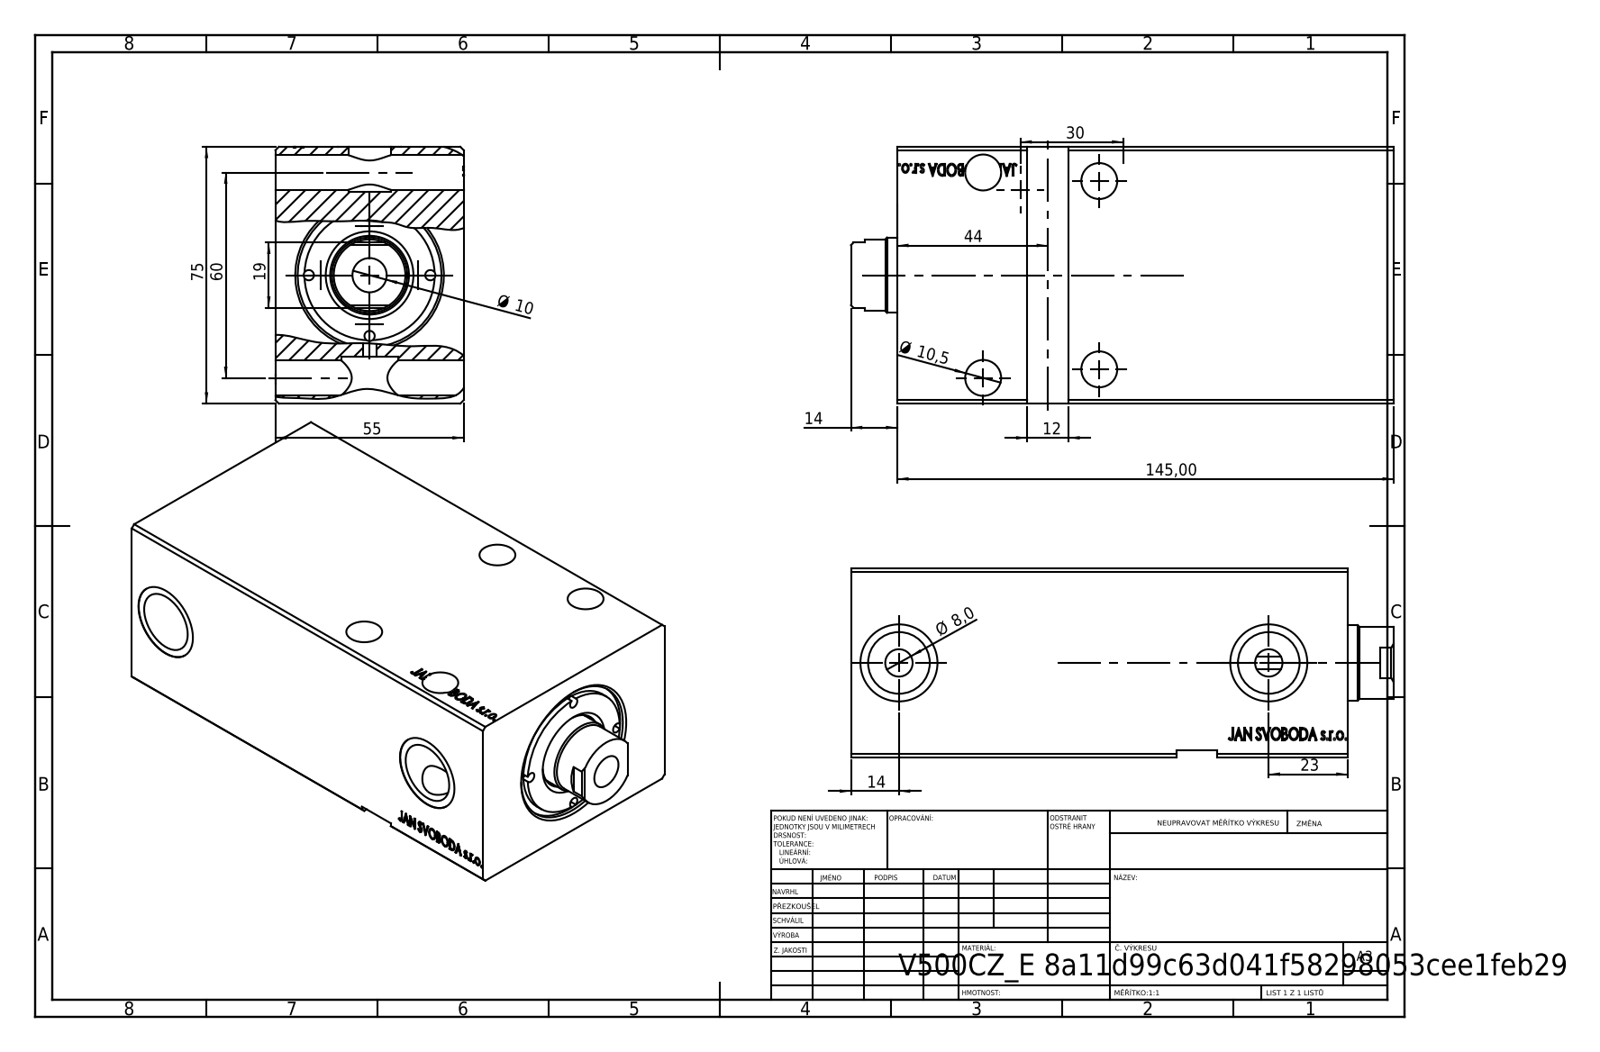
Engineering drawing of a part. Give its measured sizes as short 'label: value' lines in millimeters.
name: V500CZ_VCP_E; V500CZ_E; V500CZ_VC_vysunovaci_E
written by: SolidWorks 2019 (CONFIG_CONTROL_DESIGN)
unit: mm
bodies: 3 solids, 800 faces (381 planar, 67 cylindrical, 352 other)
size: 158.5 × 75 × 55
volume: 534 661 mm³; area: 82 979 mm²
holes: 4× ⌀3, 4× ⌀10.5, 4× ⌀18, 4× ⌀22.5, 2× ⌀5.5, 2× ⌀8, 1× ⌀10, 1× ⌀22, 1× ⌀23, 1× ⌀32, 1× ⌀36, 1× ⌀42
bosses: 1× ⌀38, 1× ⌀20.92
face distances: 55, 75, 145, 115, 30, 144.8, 29.8, 11.8, 103.2, 133
hole spacings: 17.75, 25.1, 34, 35.5, 66.75, 1, 3, 55
